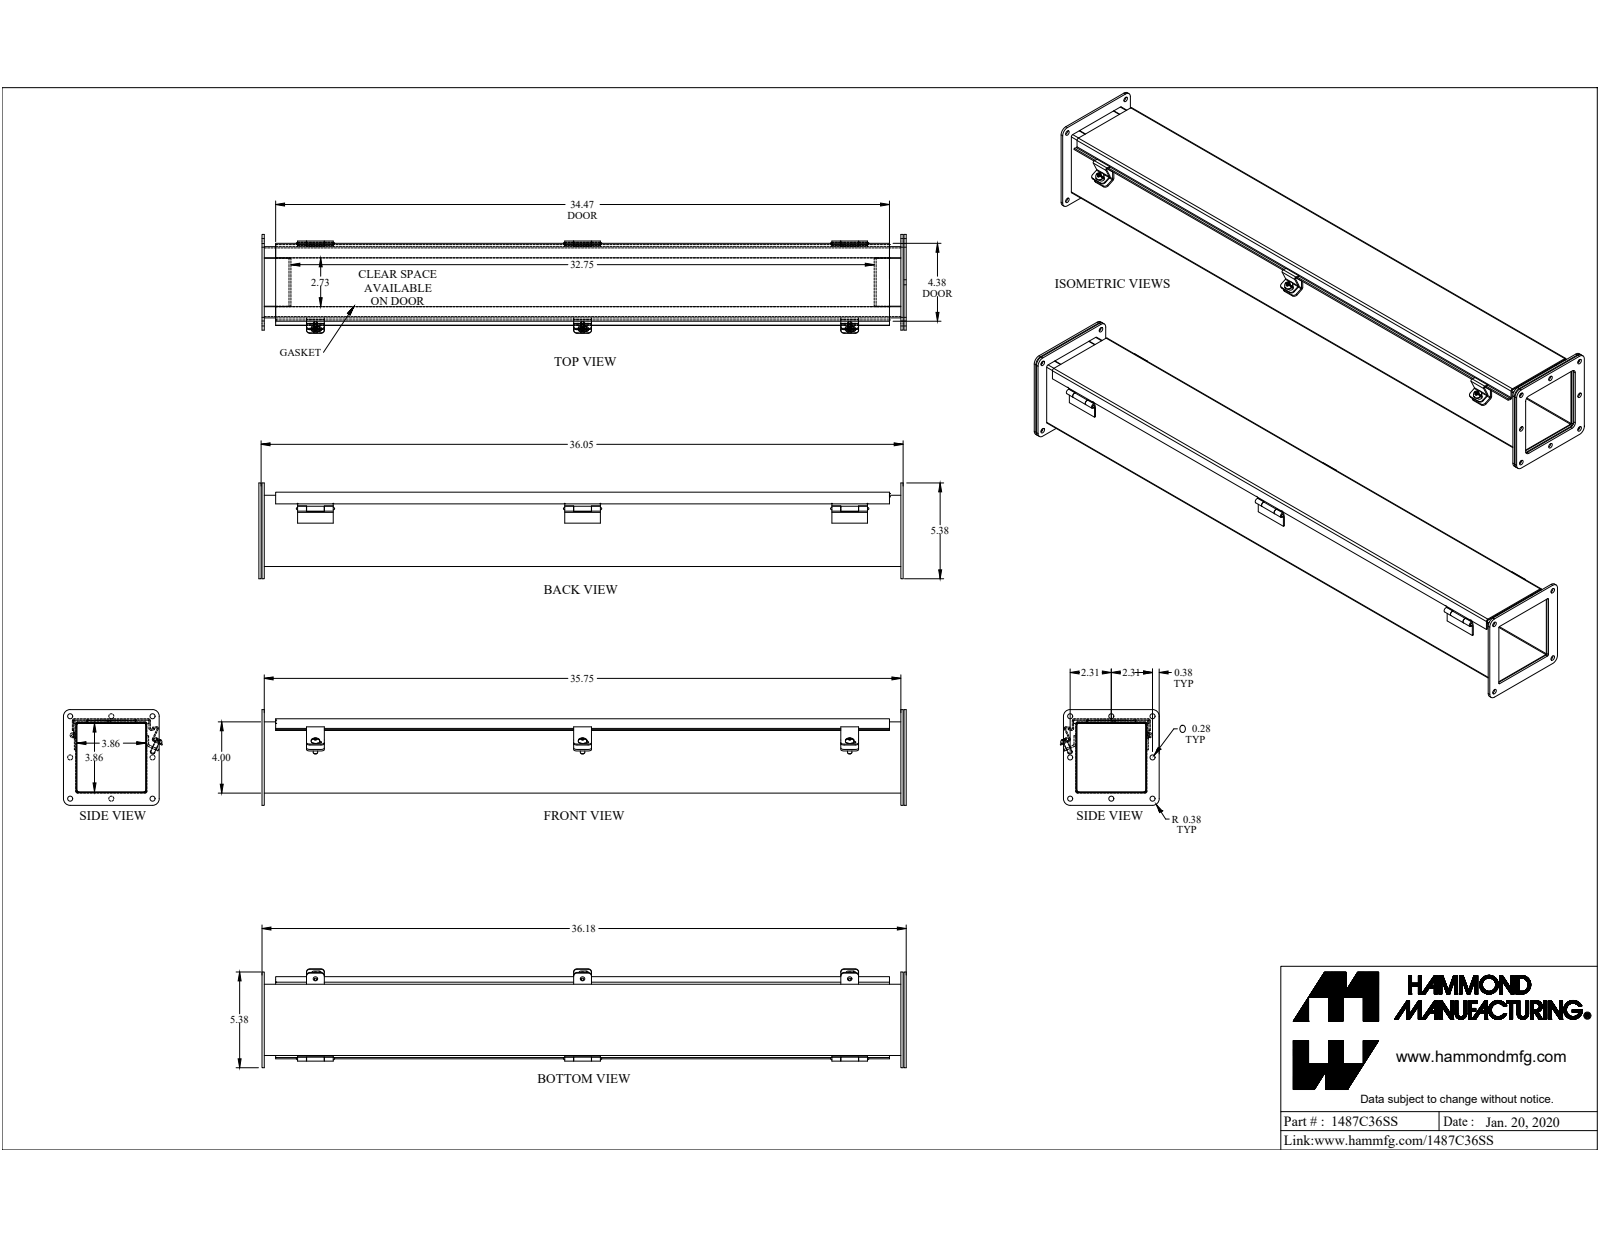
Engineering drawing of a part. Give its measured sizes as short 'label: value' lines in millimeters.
name: 1487C36SS
written by: SolidWorks 2019 (CONFIG_CONTROL_DESIGN)
unit: mm
bodies: 33 solids, 666 faces (429 planar, 176 cylindrical, 61 other)
size: 928.3 × 141 × 136.5
volume: 1 070 000 mm³; area: 1 065 000 mm²
holes: 8× ⌀7.1, 3× ⌀5.4, 1× ⌀4.7, 1× ⌀5, 1× ⌀6.6, 1× ⌀8.9
bosses: 4× ⌀6.4, 3× ⌀12.2, 1× ⌀12.7, 1× ⌀8.6, 1× ⌀4.6
rounds: 12× R4.8, 8× R9.5, 7× R0.9, 7× R2.7, 6× R0.5, 6× R0.8, 6× R3.6, 4× R1.6
face distances: 1.8, 99.8, 104.1, 101.6, 97.9, 106, 102.3, 4.7, 4.4, 6.6
hole spacings: 58.8, 131.3, 117.5, 117.5, 58.7, 83.1, 83.1, 131.3
